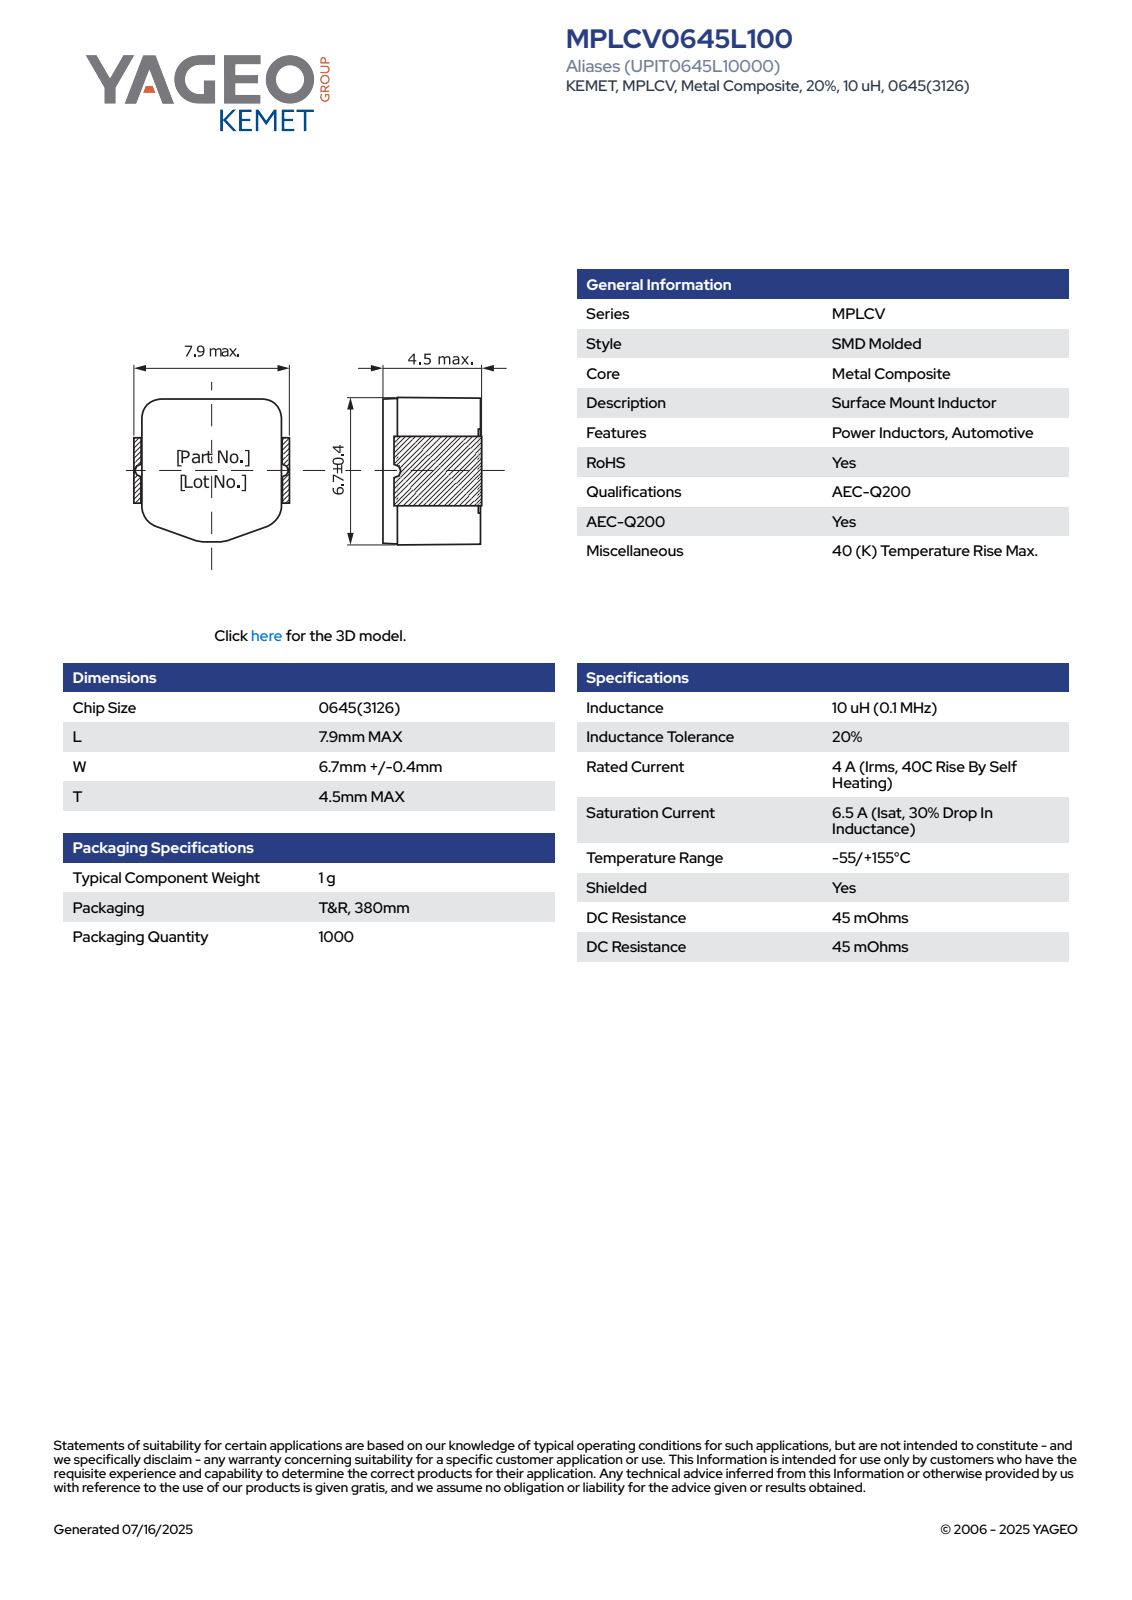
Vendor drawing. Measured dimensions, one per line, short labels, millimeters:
name: IS_MPLCV_0645(3126)_L7.9W7.1T4.5
written by: SolidWorks 2014 (AUTOMOTIVE_DESIGN)
unit: mm
bodies: 4 solids, 116 faces (95 planar, 21 cylindrical, 0 other)
size: 7.9 × 7.1 × 4.5
volume: 219 mm³; area: 256 mm²
rounds: 4× R1, 2× R0.6, 1× R0.15
face distances: 4.5, 7.7, 7.5, 7.8, 7.6, 4.4, 7.9, 7.1, 3, 2.9
